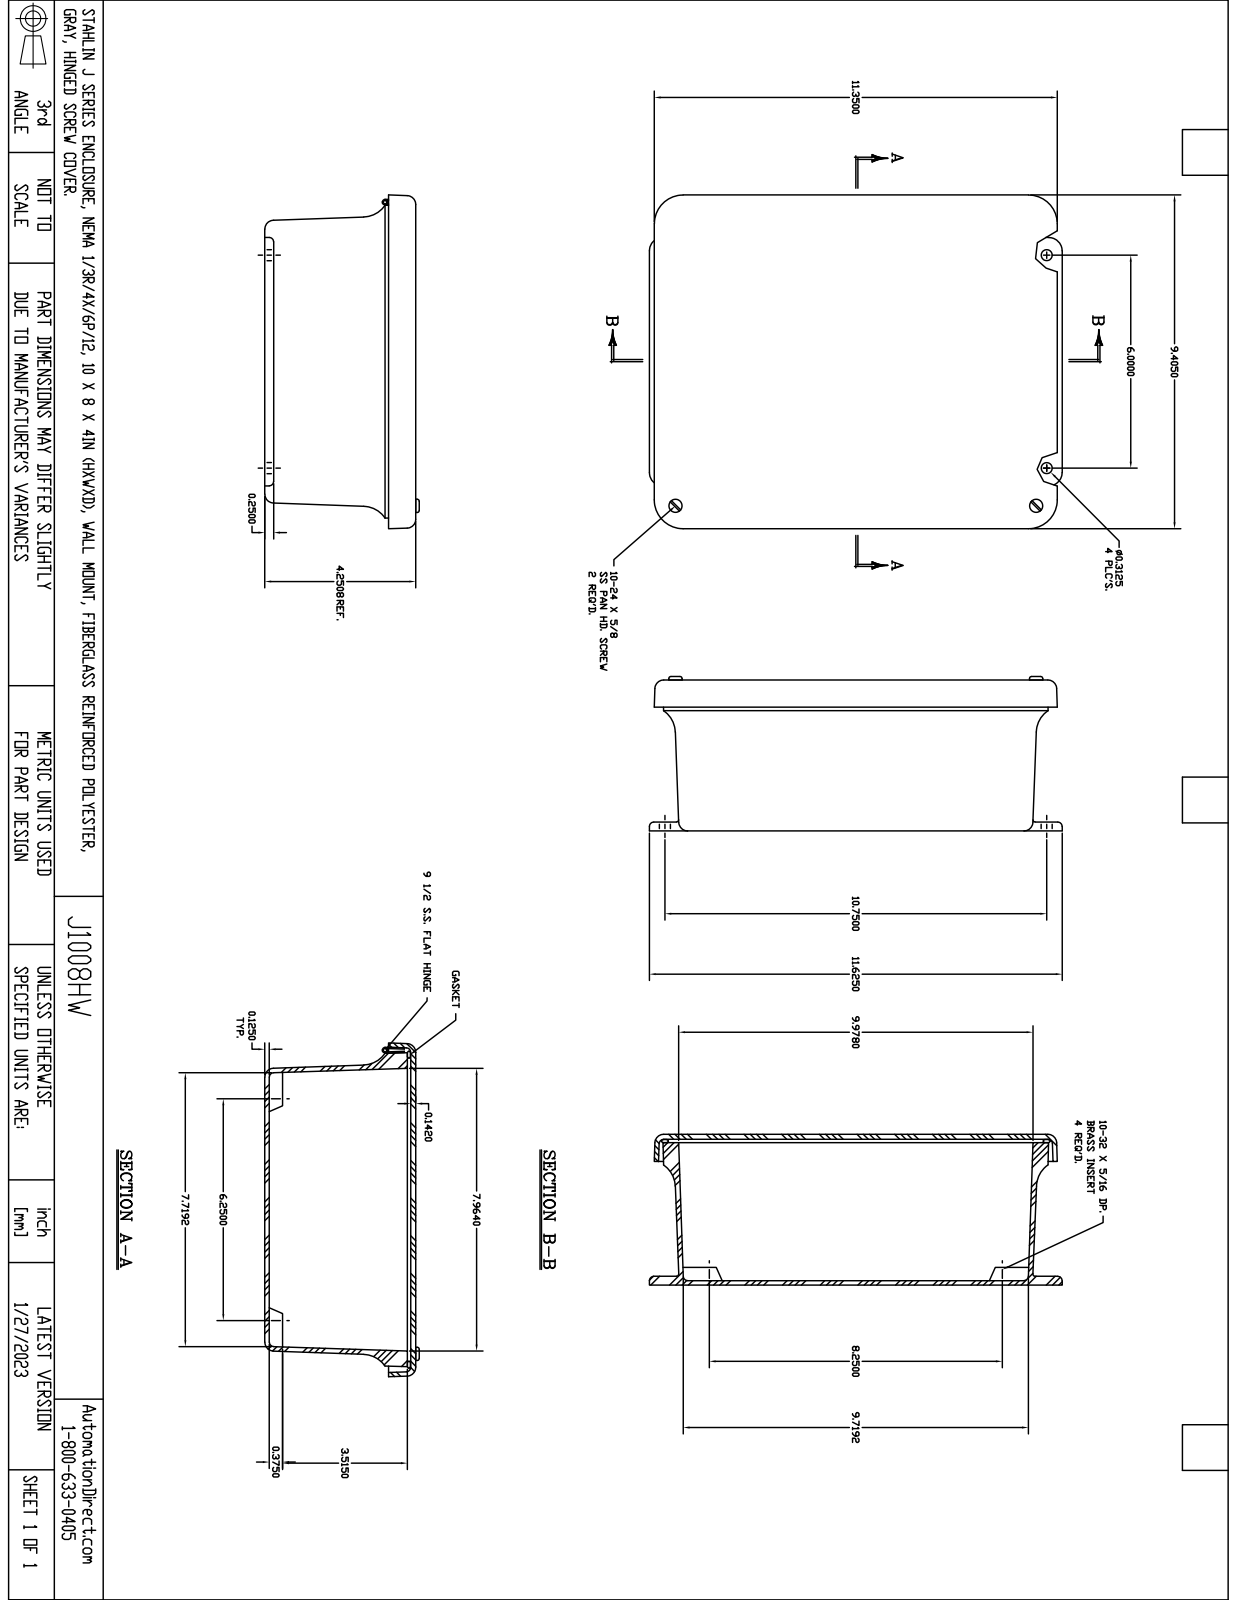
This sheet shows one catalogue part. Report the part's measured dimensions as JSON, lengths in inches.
{"part_name": "M1008HW", "step_written_by": "SolidWorks 2018 (AUTOMOTIVE_DESIGN)", "units": "inches", "bodies": {"solids": 22, "faces": 759, "planar": 259, "cylindrical": 291, "other": 209}, "overall_size": [11.625, 9.433, 4.366], "volume_in3": 60.59, "surface_area_in2": 805.5, "round_holes": [[0.131, 8], [0.14, 8], [0.152, 5], [0.156, 4], [0.218, 4], [0.145, 2], [0.085, 1], [0.085, 1]], "round_bosses_or_shafts": [[0.25, 8], [0.27, 6], [0.125, 5], [0.125, 3], [0.19, 2], [0.156, 2], [0.155, 1]], "partial_cylinders_radius": [[0.031, 20], [0.125, 12], [0.25, 8], [0.2, 7], [0.375, 4], [0.75, 4], [0.063, 2]], "face_to_face_distances": [0.142, 4.093, 4.235, 0.125, 3.968, 4.11, 0.12, 3.89, 0.22, 4.015], "hole_center_spacings": [6, 3, 0.25, 2.5, 2.75, 6.25, 1.337, 3.25]}
